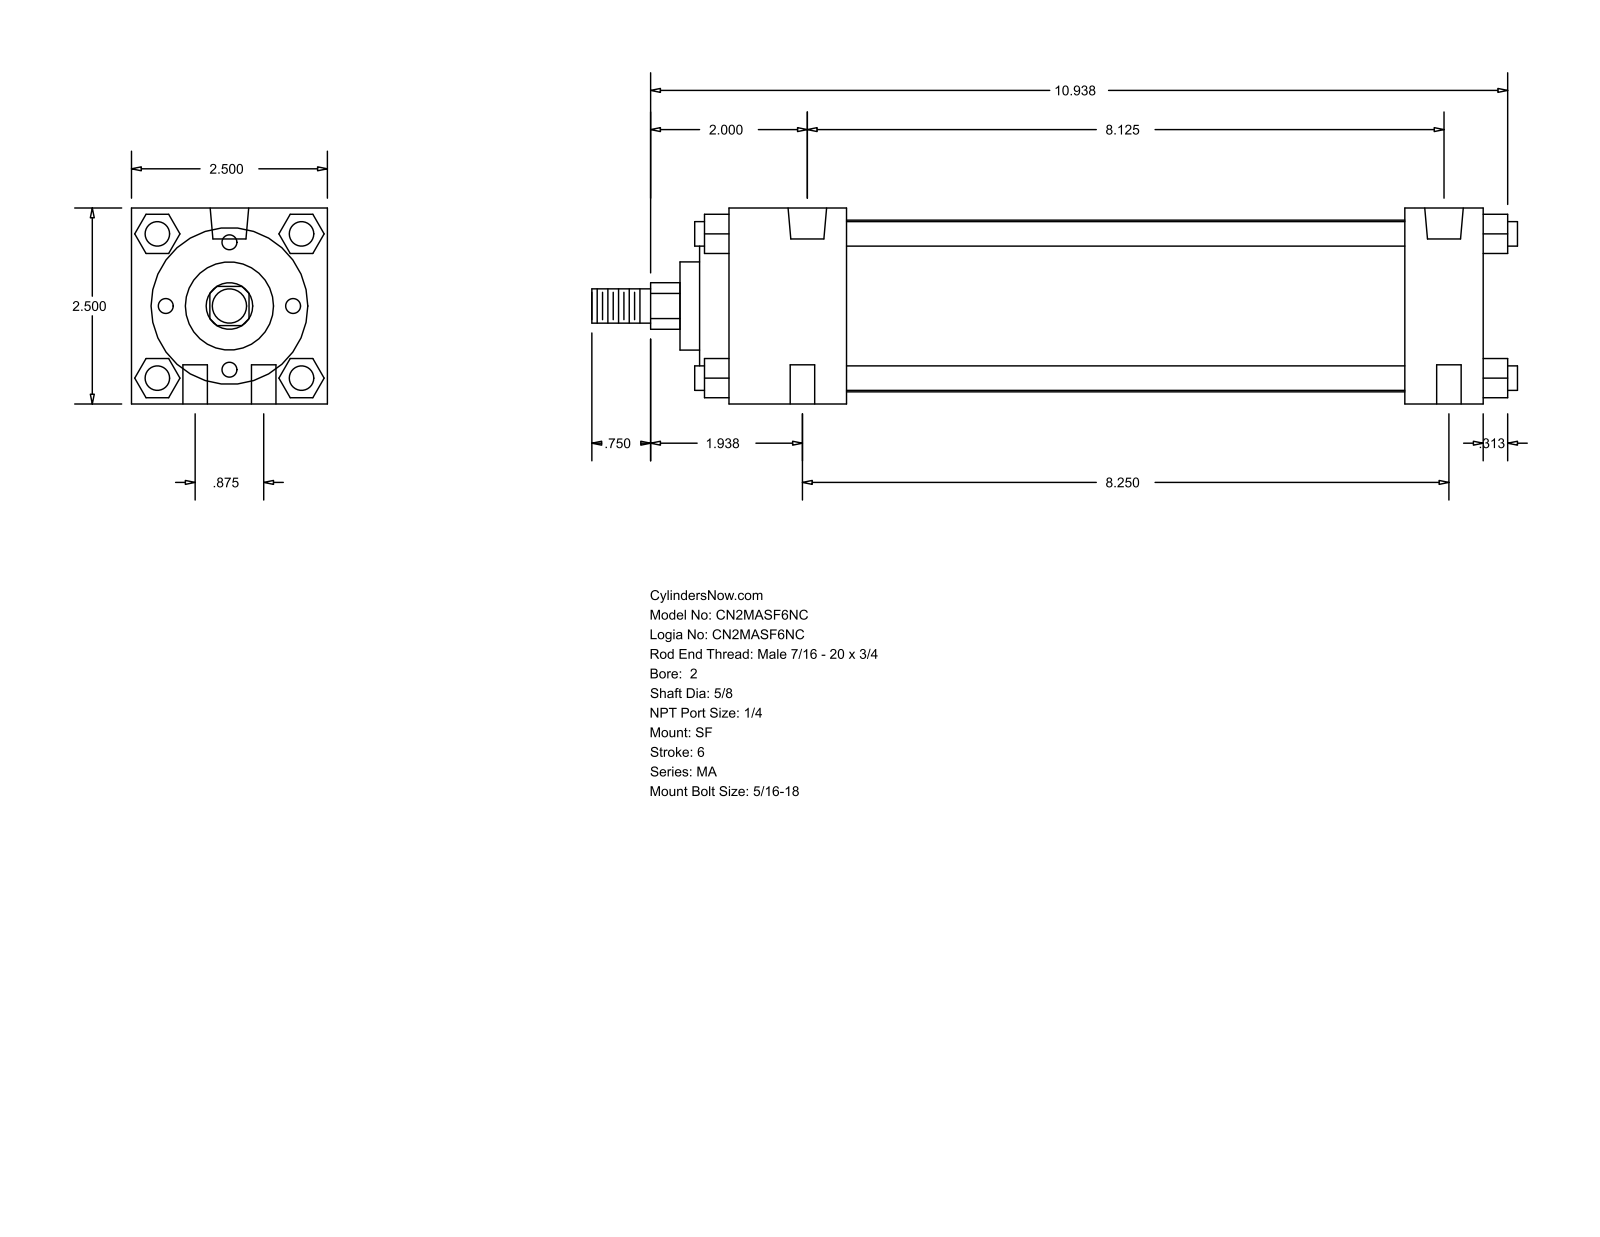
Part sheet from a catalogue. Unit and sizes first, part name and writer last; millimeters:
Units: millimetres
Overall size (bounding box): 300.04 × 63.5 × 63.5
Round holes (diameter × count): ⌀7.94 ×6, ⌀12.49 ×2
Round bosses / shafts (diameter × count): ⌀7.94 ×4, ⌀55.63 ×1, ⌀50.8 ×1, ⌀28.57 ×1, ⌀15.88 ×1, ⌀11.11 ×1
Partial cylindrical surfaces — rounded edges, fillets, slot ends (radius × count): R7.54 ×1
Main face-to-face distances: 63.5, 12.7, 38.1, 244.48, 219.07, 25.41, 180.97, 206.38, 9.52, 47.62
Hole centre spacings: 11.22, 22.22, 206.38, 208.26, 208.27, 209.55, 210.72
Bodies: 0 solids, 126 faces (95 planar, 31 cylindrical, 0 other)
Part name (STEP PRODUCT): MA_SF__0200_0.625
STEP written by: GSSL Pune (CONFIG_CONTROL_DESIGN)
